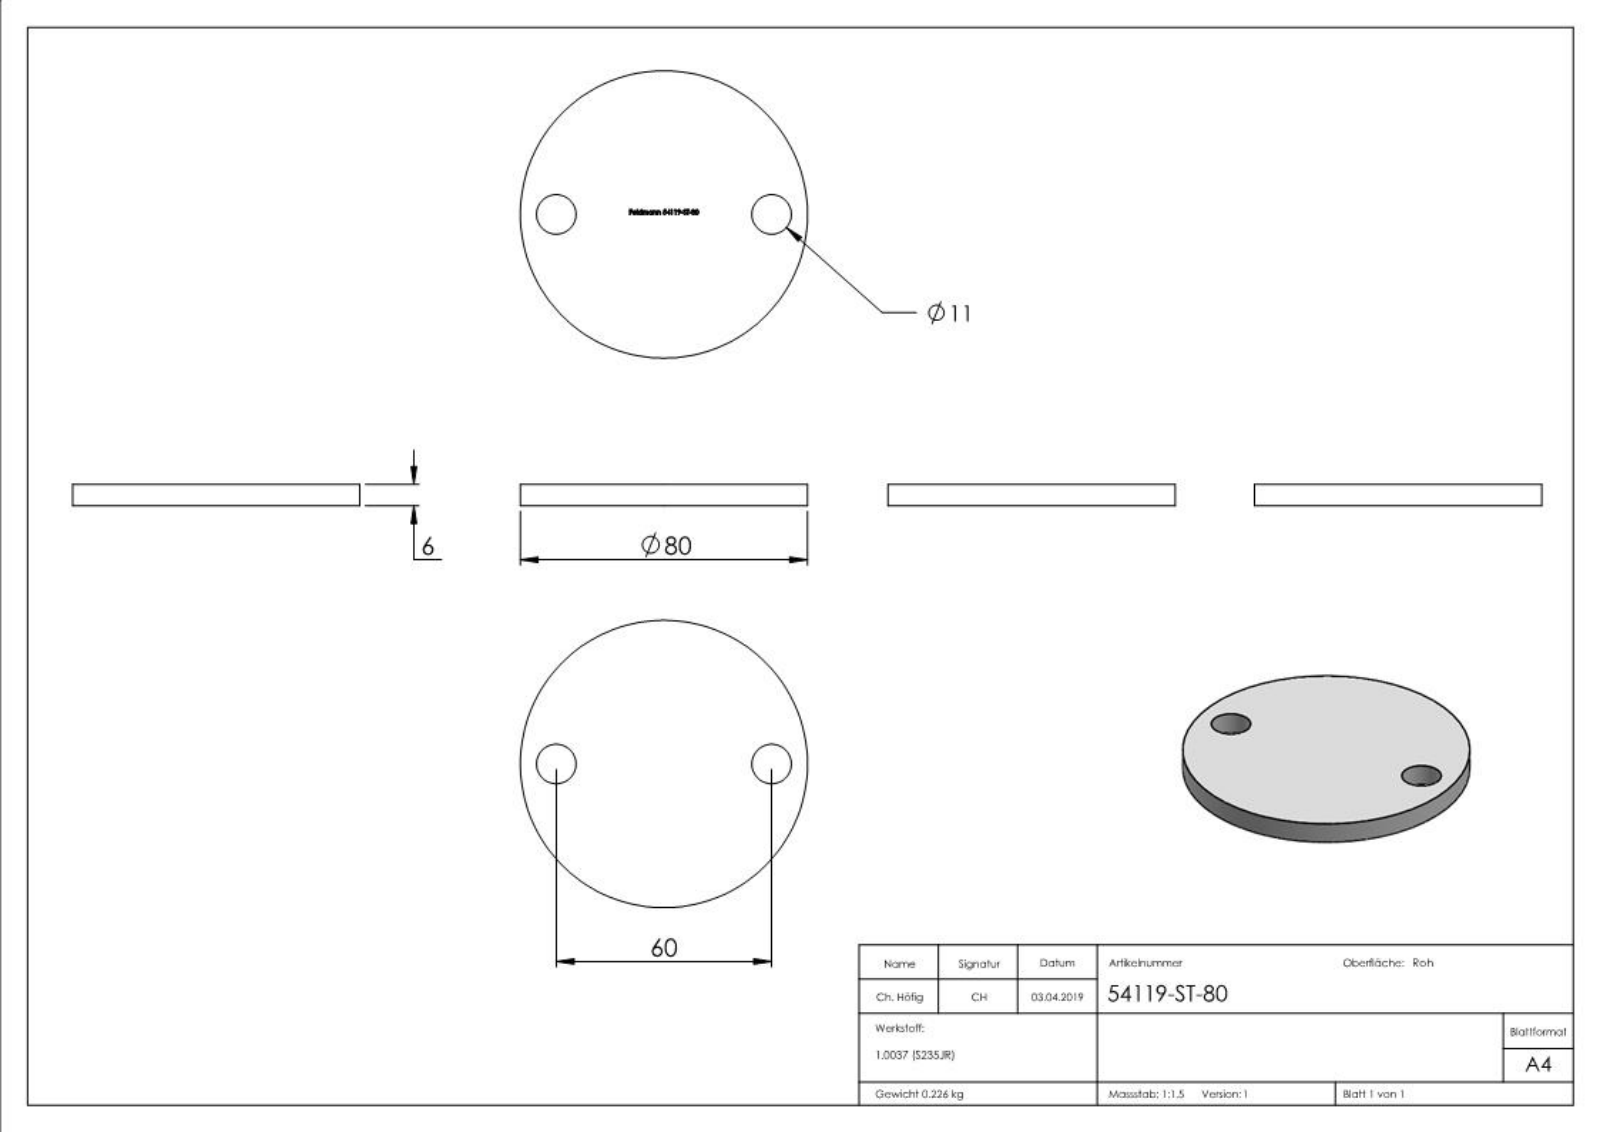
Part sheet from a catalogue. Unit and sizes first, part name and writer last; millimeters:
Units: millimetres
Overall size (bounding box): 80 × 80 × 6
Round holes (diameter × count): ⌀11 ×2
Round bosses / shafts (diameter × count): ⌀80 ×1
Main face-to-face distances: 6, 5.9, 1.01, 9.72, 10.73, 0.88, 2.97, 14.14, 4.42, 3.41
Hole centre spacings: 60
Volume: 29 018 mm³ · Surface area: 11 605 mm²
Bodies: 1 solid, 247 faces (135 planar, 6 cylindrical, 106 other)
Part name (STEP PRODUCT): 54119-ST-80
STEP written by: SolidWorks 2015 (CONFIG_CONTROL_DESIGN)
